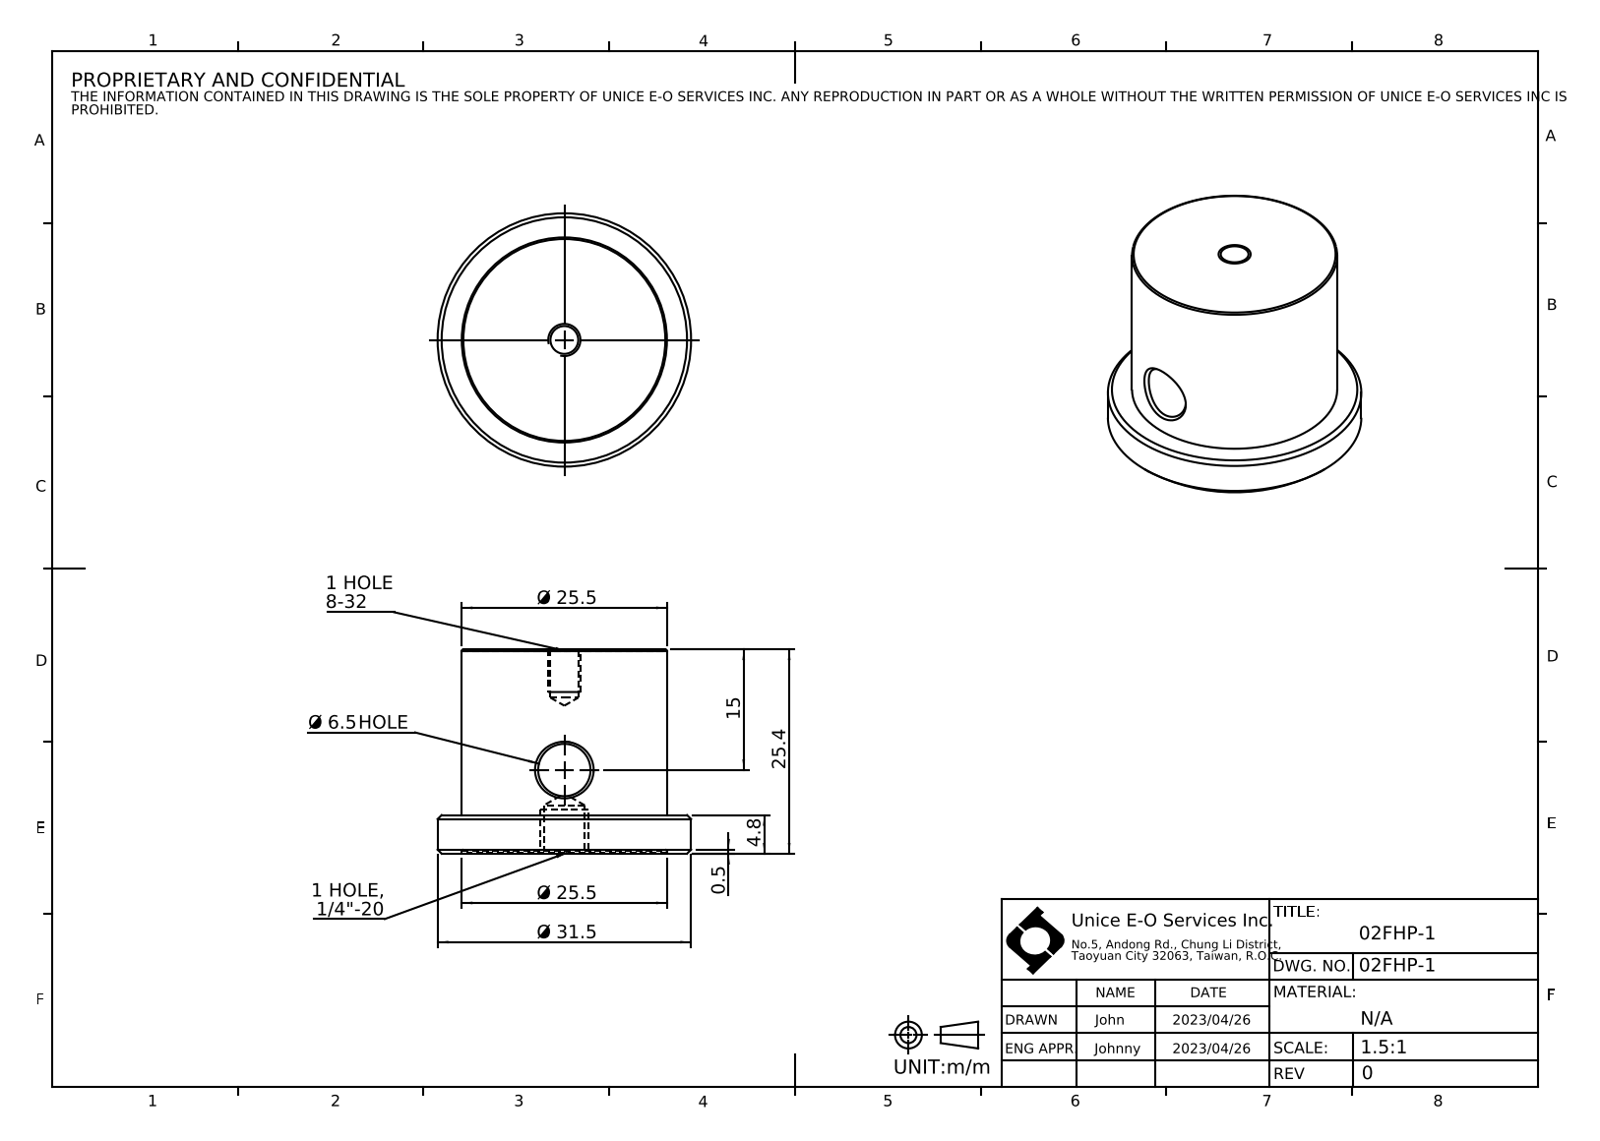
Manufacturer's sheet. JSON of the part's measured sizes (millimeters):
{"part_name": "02FHP-1", "step_written_by": "SolidWorks 2016 (CONFIG_CONTROL_DESIGN)", "units": "millimeters", "bodies": {"solids": 1, "faces": 34, "planar": 4, "cylindrical": 12, "other": 18}, "overall_size": [31.5, 31.5, 25.4], "volume_mm3": 12957, "surface_area_mm2": 4239, "round_holes": [[3.45, 1], [5.11, 1], [6.5, 1], [25.5, 1]], "round_bosses_or_shafts": [[31.5, 1]], "face_to_face_distances": [24.9, 4.3, 20.6, 0.5, 4.8, 25.4]}
